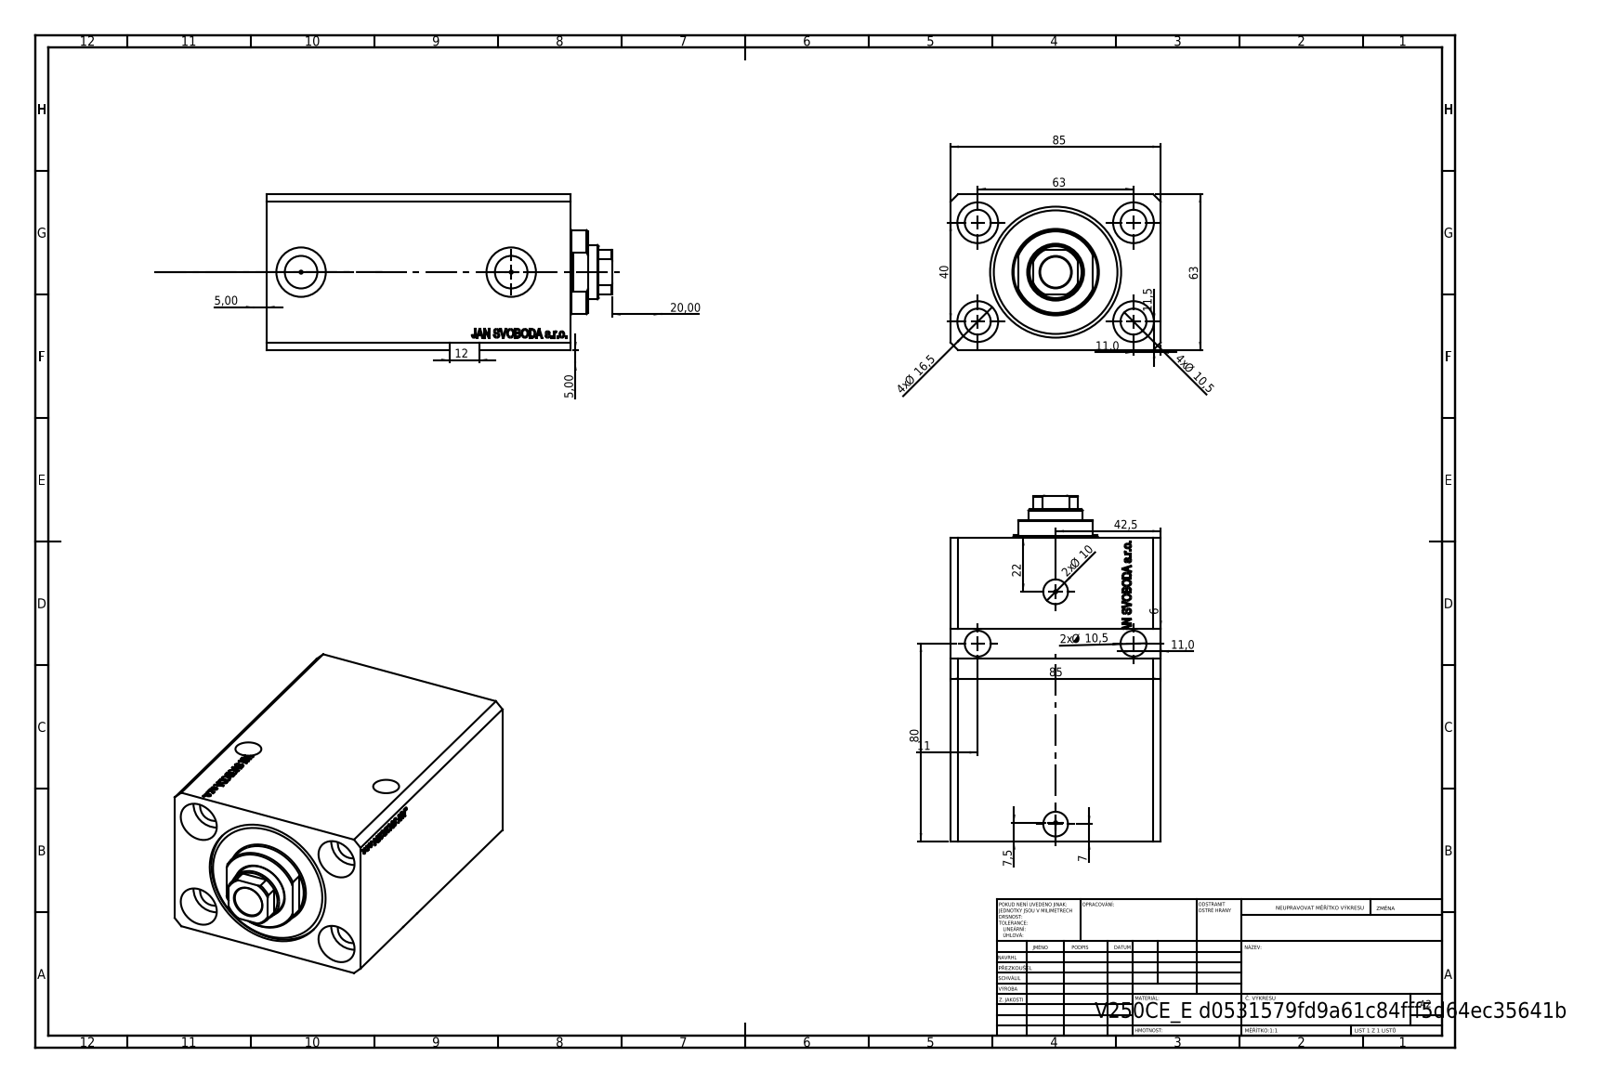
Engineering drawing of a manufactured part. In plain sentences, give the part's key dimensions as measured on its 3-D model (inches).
The part is named "V250CE_E_Body; V250CE_C_VCP; V250CE_VC_E". Its 3-D file was written by "SolidWorks 2019 (CONFIG_CONTROL_DESIGN)". It is 3 solids with 917 faces: 459 planar, 84 cylindrical and 374 other. Overall it measures 5.508 by 3.346 by 2.48 inches. Its volume is 33.6 cubic inches and its surface area 167.2 square inches. Round holes: 6 of diameter 0.413, 4 of diameter 0.049, 4 of diameter 0.65, 2 of diameter 0.394, 2 of diameter 0.518, 2 of diameter 0.787, 1 of diameter 0.492, 1 of diameter 0.866, 1 of diameter 1.575, 1 of diameter 2.087. Round bosses or shafts: 1 of diameter 1.339. Partial cylindrical surfaces (rounded edges, fillets, slot ends): 1 of radius 0.413. The main face-to-face distances are 2.48, 3.346, 4.843, 3.776, 1.067, 3.327, 0.449, 4.394, 0.433, 4.409. The hole center spacings are 1.469, 2.48, 1.491, 1.575, 2.938, 3.111, 3.13, 0.021.
